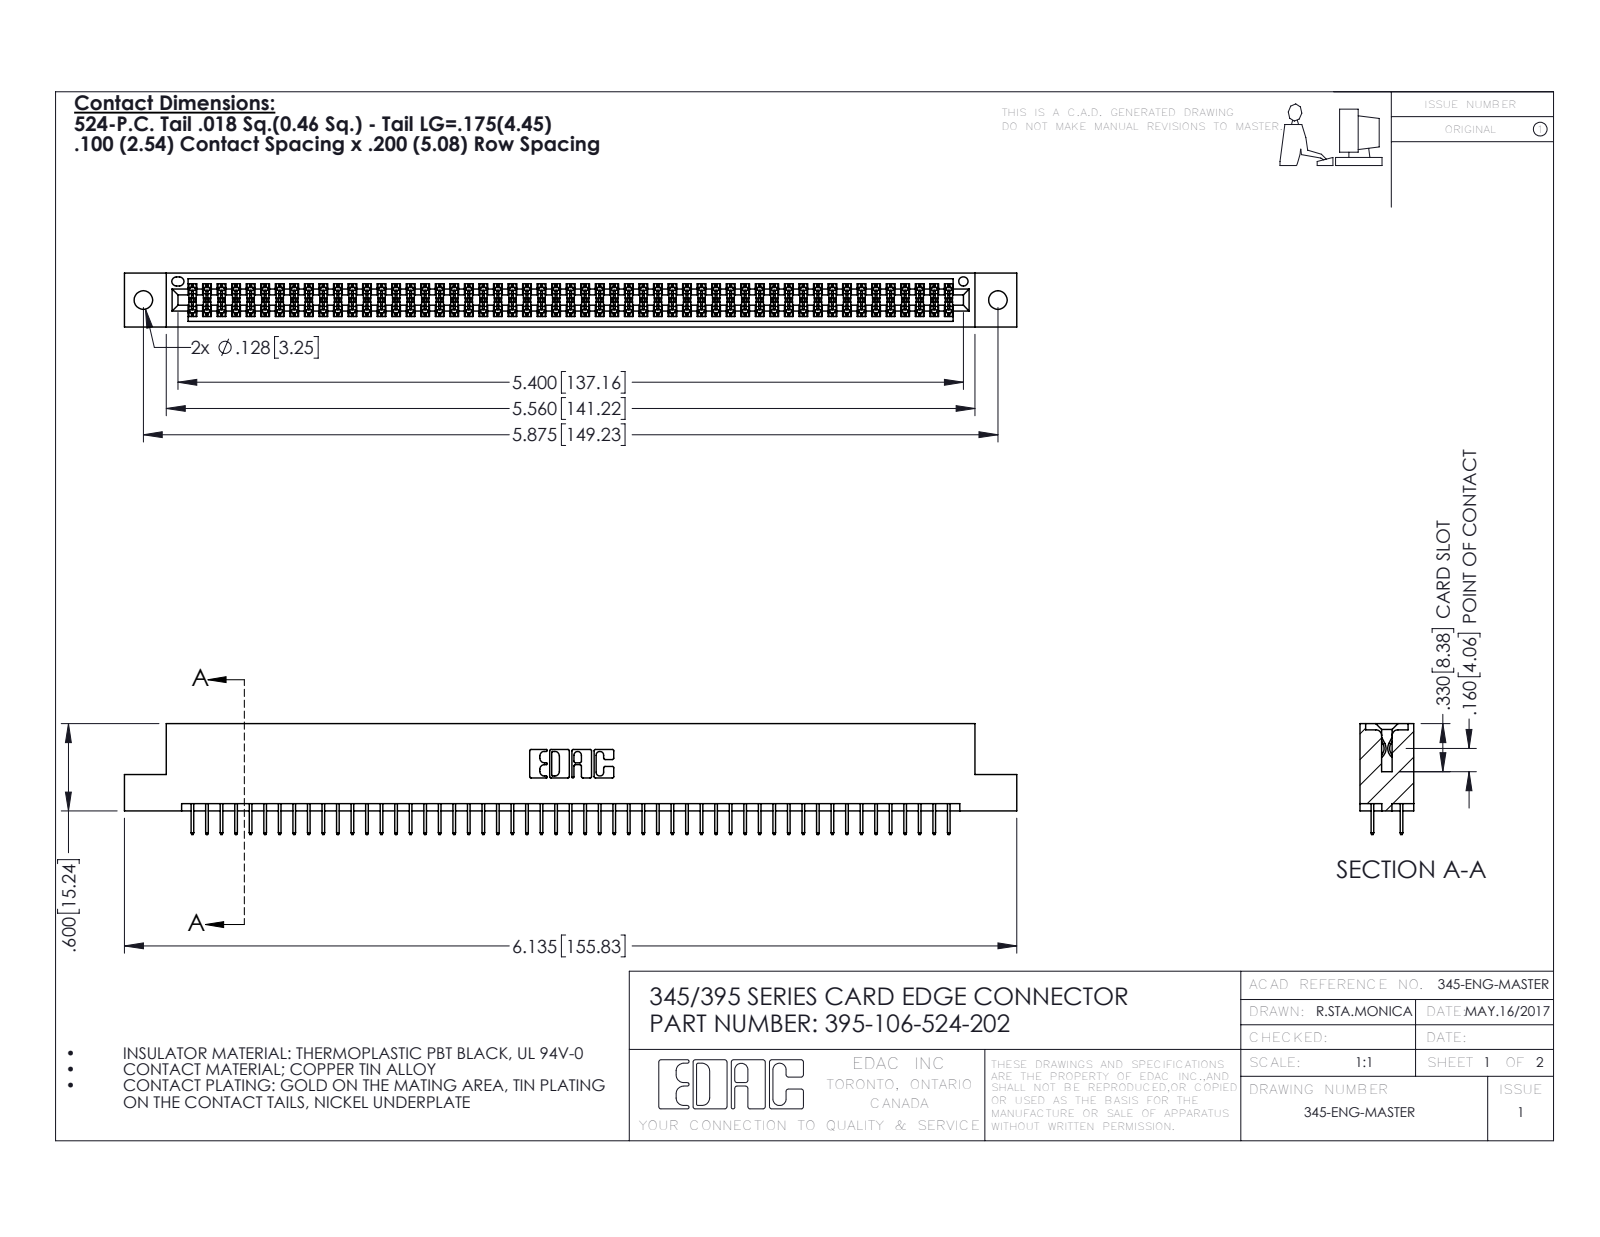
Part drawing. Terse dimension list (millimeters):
name: 395-106-524-202; 345 Part_Flush Mounting Lugs - 0.128 Dia; 345-292-001_345-293-124
written by: SolidWorks 2016 (CONFIG_CONTROL_DESIGN)
unit: mm
bodies: 107 solids, 5850 faces (4214 planar, 1636 cylindrical, 0 other)
size: 155.8 × 19.4 × 9.4
volume: 15 000 mm³; area: 21 750 mm²
holes: 2× ⌀3.3, 1× ⌀1.6
rounds: 159× R0.2, 22× R0.3, 6× R0.2, 6× R0.8, 3× R0.7, 2× R0.4, 2× R0.5, 2× R0.6
face distances: 7.6, 1.8, 5.1, 9.4, 2.5, 6.9, 0.6, 5.7, 1.8, 4.4
hole spacings: 6.9, 143.2, 149.2
